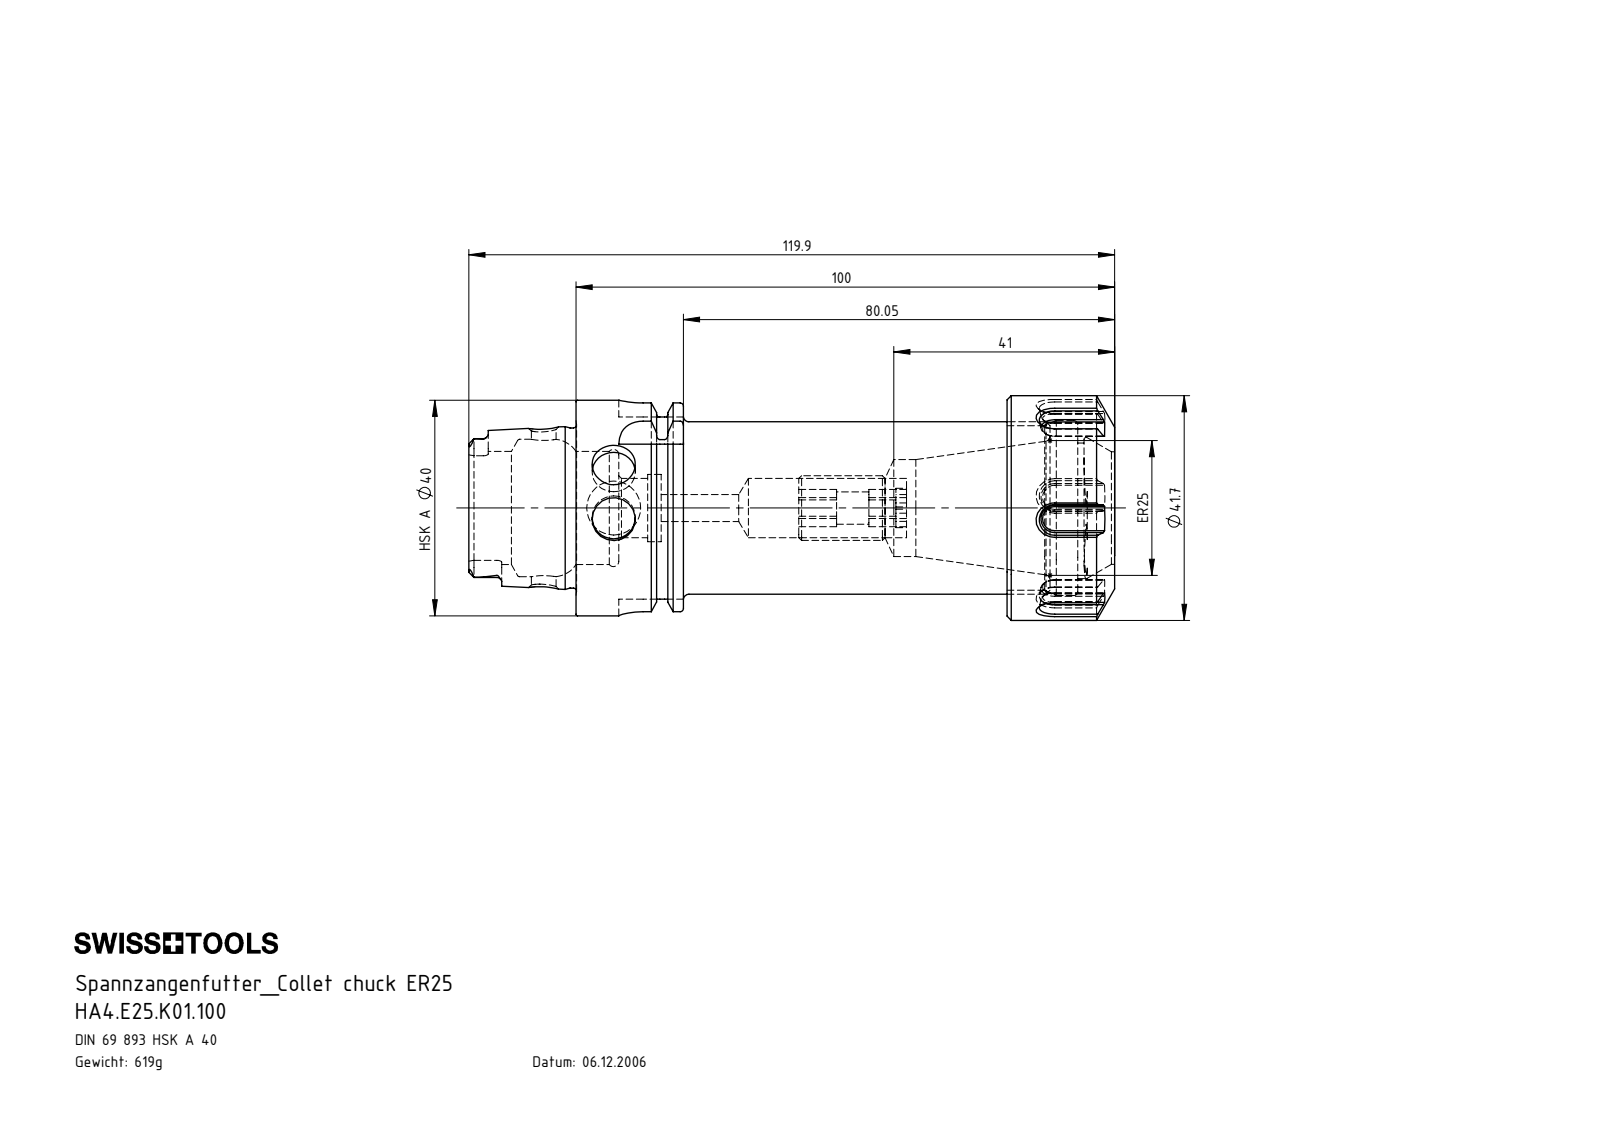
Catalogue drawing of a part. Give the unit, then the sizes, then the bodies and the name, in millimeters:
Units: millimetres
Overall size (bounding box): 119.9 × 41.7 × 41.7
Round holes (diameter × count): ⌀8 ×2, ⌀4.6 ×1, ⌀5 ×1, ⌀6 ×1, ⌀10 ×1, ⌀11 ×1, ⌀12.5 ×1, ⌀18 ×1, ⌀20.9 ×1, ⌀21 ×1, ⌀25.5 ×1, ⌀30.5 ×1
Round bosses / shafts (diameter × count): ⌀41.7 ×1, ⌀40 ×1, ⌀34.75 ×1, ⌀32 ×1, ⌀29.71 ×1, ⌀12 ×1
Partial cylindrical surfaces — rounded edges, fillets, slot ends (radius × count): R0.9 ×6, R1.88 ×4, R4.5 ×4, R12.17 ×2
Main face-to-face distances: 20, 80, 80.05, 12, 100, 93.15, 13.15, 6.85, 19.95, 60.05
Volume: 78 843 mm³ · Surface area: 26 789 mm²
Bodies: 3 solids, 314 faces (131 planar, 71 cylindrical, 112 other)
Part name (STEP PRODUCT): HA4.E25.K01.100; E25-ER1.001.020; ERU-AN5.K01.020_A; HA4-E25.K01.100_B_Fertigbearbeitung
STEP written by: SolidWorks 2017 (CONFIG_CONTROL_DESIGN)
